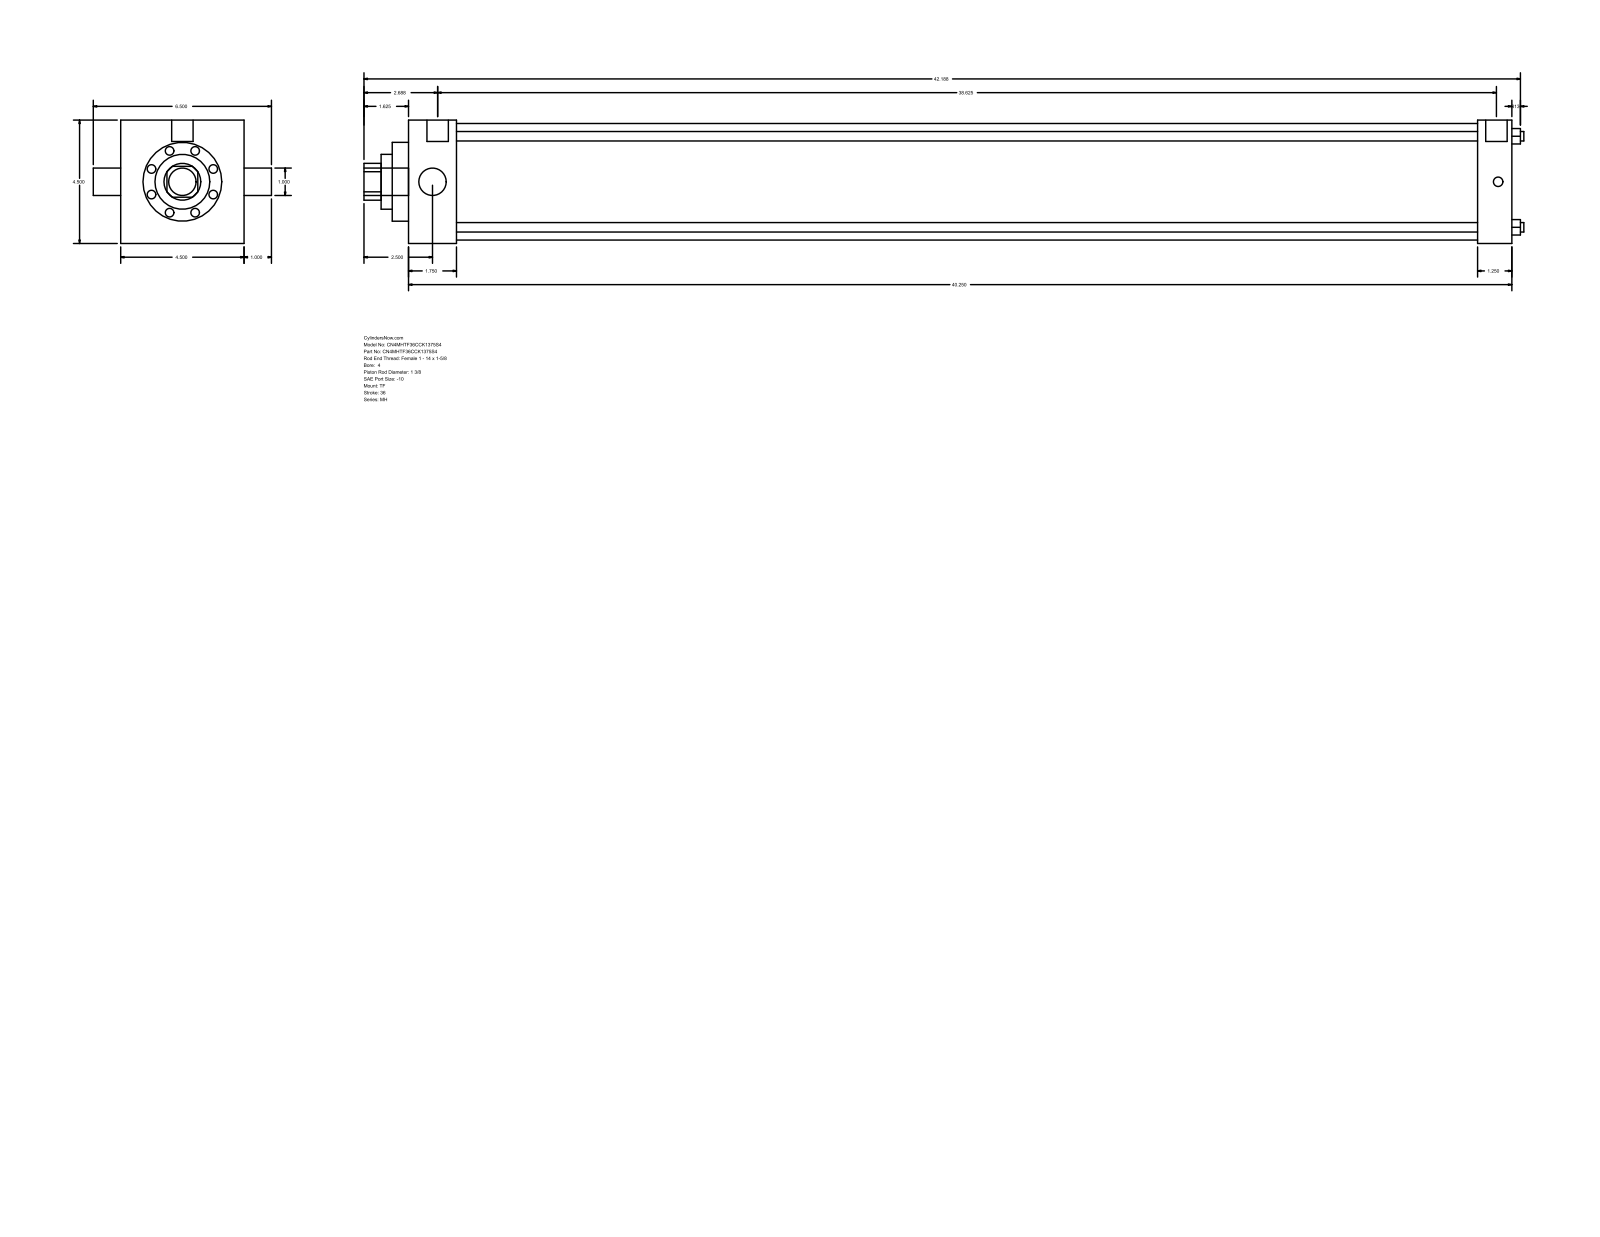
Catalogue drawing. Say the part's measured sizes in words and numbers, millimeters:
The part is named "MH_TF__0400_1.375". Its 3-D file was written by "GSSL Pune (CONFIG_CONTROL_DESIGN)". It is 0 solids with 86 faces: 61 planar, 25 cylindrical and 0 other. Overall it measures 1074.74 by 165.1 by 114.3 millimeters. Round holes: 4 of diameter 8.76, 1 of diameter 25.4, 1 of diameter 34.92, 1 of diameter 50.8, 1 of diameter 73.03, 1 of diameter 107.95. Round bosses or shafts: 3 of diameter 8.73, 2 of diameter 19.84, 1 of diameter 25.4. Partial cylindrical surfaces (rounded edges, fillets, slot ends): 1 of radius 17.06. The main face-to-face distances are 114.3, 1022.35, 44.45, 977.9, 990.61, 946.16, 31.74, 15.08, 59.53, 1005.69. The hole center spacings are 59.62, 84.32, 119.25.
